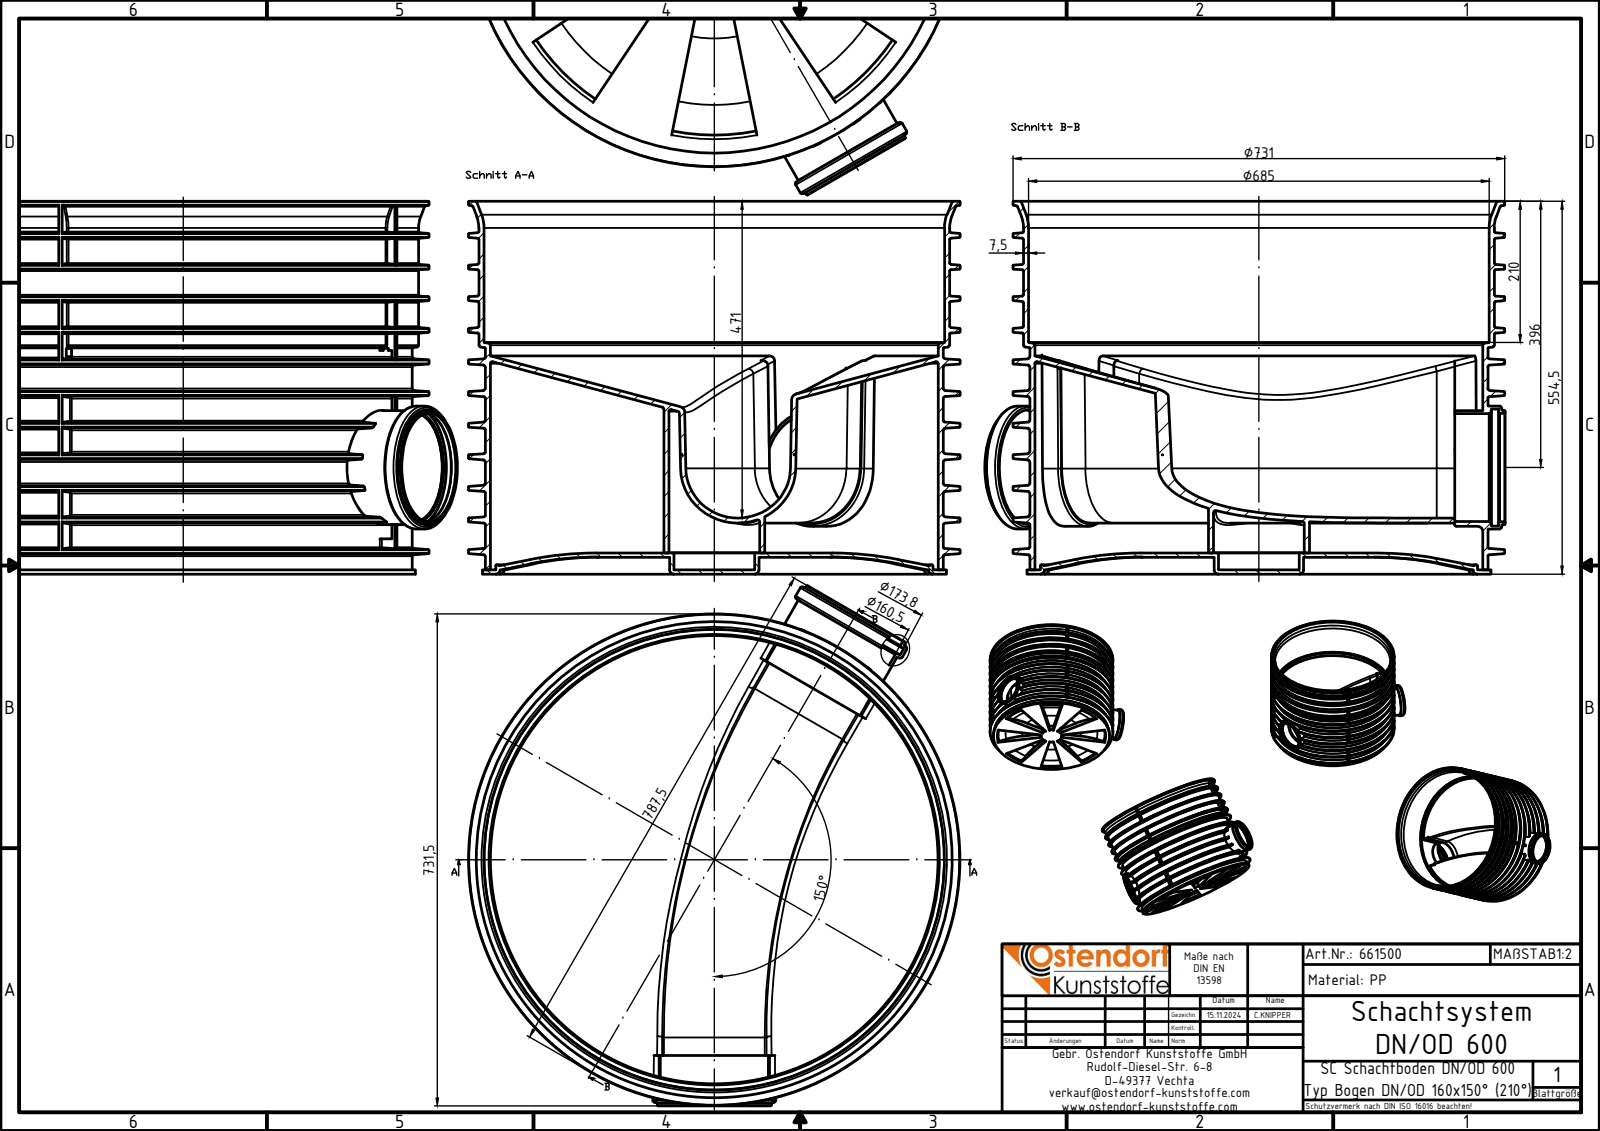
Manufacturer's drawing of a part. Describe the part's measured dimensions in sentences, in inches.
The part is named "661500z; 661500 Schachtboden DN600 Grundkörper; 661500 Schacht DN600 Boden". Its 3-D file was written by "Autodesk Inventor 2024 (AUTOMOTIVE_DESIGN)". It is 2 solids with 1480 faces: 159 planar, 258 cylindrical and 1063 other. Overall it measures 30.455 by 28.78 by 21.831 inches. Its volume is 1 420 cubic inches and its surface area 8 573 square inches. Round holes: 2 of diameter 6.319, 2 of diameter 6.331, 2 of diameter 6.843, 1 of diameter 4.724, 1 of diameter 5.315, 1 of diameter 6.327, 1 of diameter 6.685, 1 of diameter 25.197, 1 of diameter 26.22, 1 of diameter 26.969. Round bosses or shafts: 2 of diameter 7.197, 2 of diameter 6.673, 1 of diameter 28.78, 1 of diameter 27.559, 1 of diameter 27.165, 1 of diameter 26.811, 1 of diameter 25.591, 1 of diameter 6.685. Partial cylindrical surfaces (rounded edges, fillets, slot ends): 16 of radius 0.079, 8 of radius 0.039, 4 of radius 0.118, 2 of radius 2.953, 2 of radius 3.248, 2 of radius 3.445, 1 of radius 2.618, 1 of radius 12.539. The main face-to-face distances are 0.256, 0.984, 1.24, 0.728, 0.295, 21.831, 21.575, 20.846, 20.591, 0.197.
